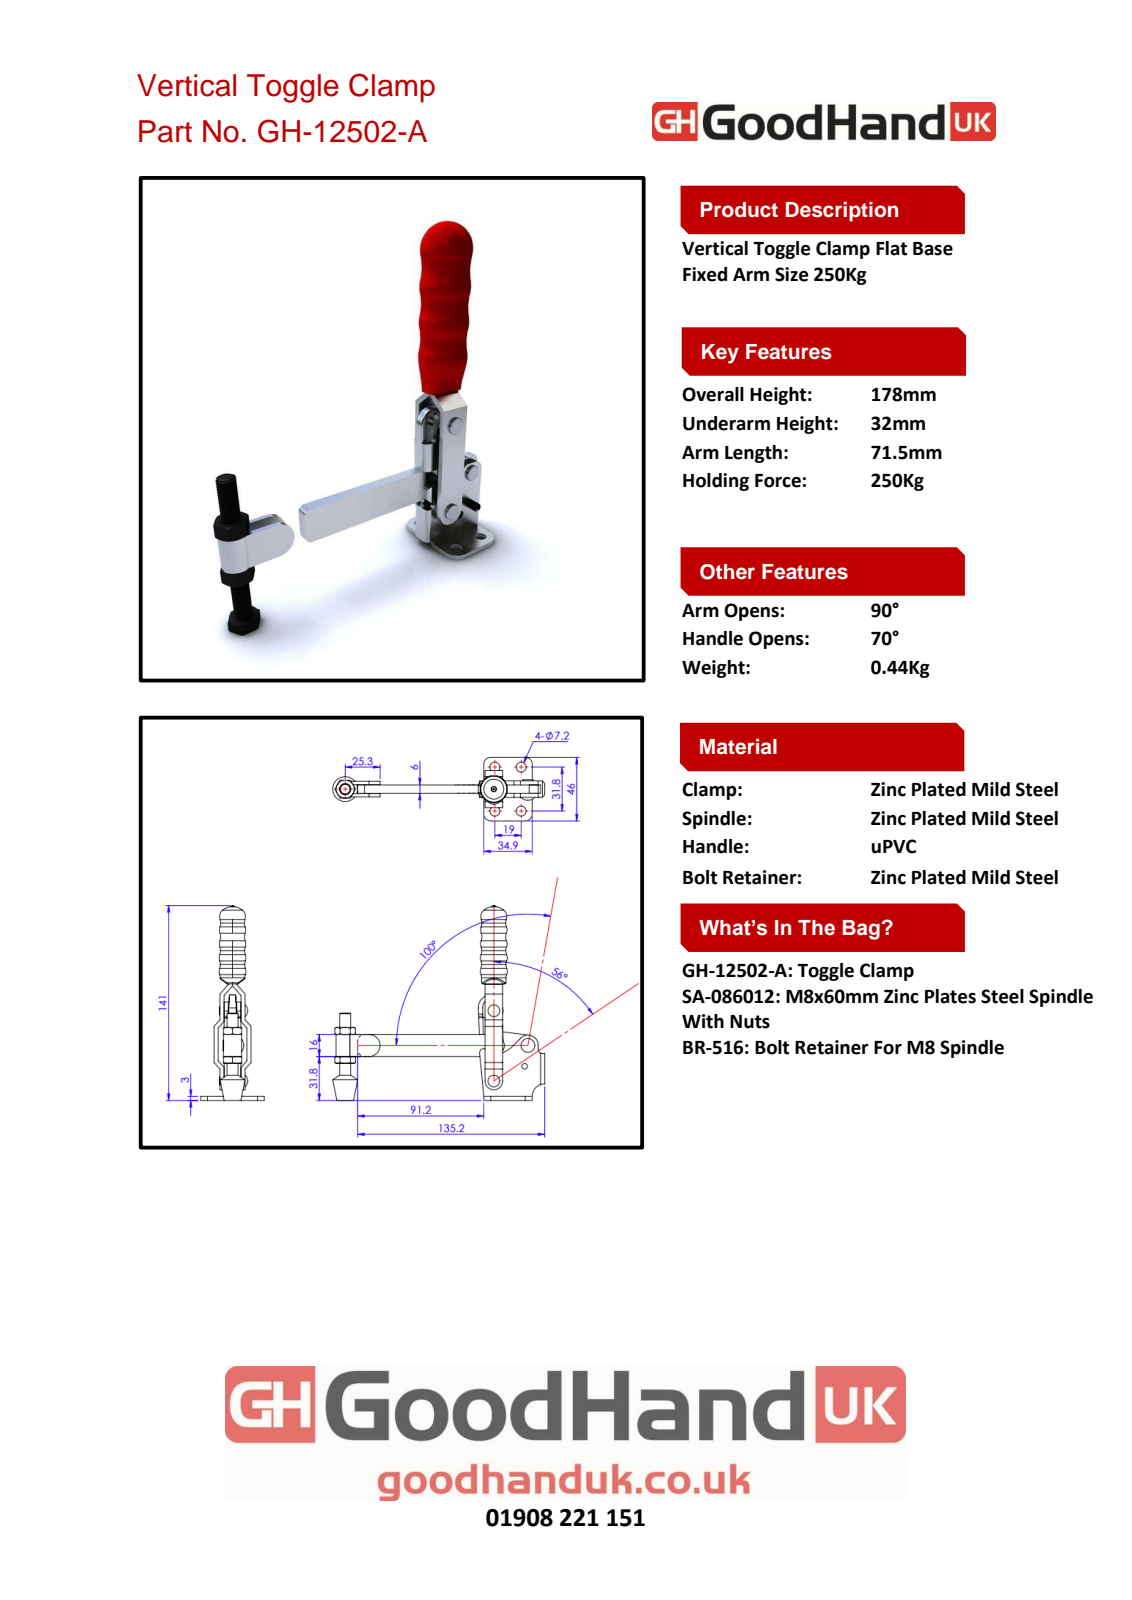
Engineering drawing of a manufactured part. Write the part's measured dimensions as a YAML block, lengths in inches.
part_name: "Group4^GH-12502-A(簡化)-1; Group1^GH-12502-A(簡化)-1; Group2^GH-12502-A(簡化)-1; Group6^GH-12502-A(簡化)-1 (+3 more)"
step_written_by: "SolidWorks 2016 (AUTOMOTIVE_DESIGN)"
units: inches
bodies: {solids: 6, faces: 356, planar: 125, cylindrical: 137, other: 94}
overall_size: [6.799, 5.703, 1.85]
volume: 4.733
surface_area: 59.82
round_holes:
  - {diameter: 0.28, count: 4}
  - {diameter: 0.197, count: 3}
  - {diameter: 0.236, count: 2}
  - {diameter: 0.268, count: 1}
  - {diameter: 0.315, count: 1}
round_bosses_or_shafts:
  - {diameter: 0.197, count: 3}
  - {diameter: 0.394, count: 2}
  - {diameter: 0.458, count: 1}
partial_cylinders:
  - {radius: 0.118, count: 6}
  - {radius: 0.295, count: 4}
  - {radius: 0.039, count: 3}
  - {radius: 0.02, count: 2}
  - {radius: 0.079, count: 2}
  - {radius: 0.098, count: 2}
  - {radius: 0.099, count: 2}
  - {radius: 0.217, count: 2}
face_to_face_distances: [0.118, 0.236, 0.354, 0.217, 0.571, 0.689, 0.098, 0.472, 0.335, 0.453]
hole_center_spacings: [0.748, 1.26, 1.465, 4.424, 5.165, 0.606, 0.833, 0.958]
